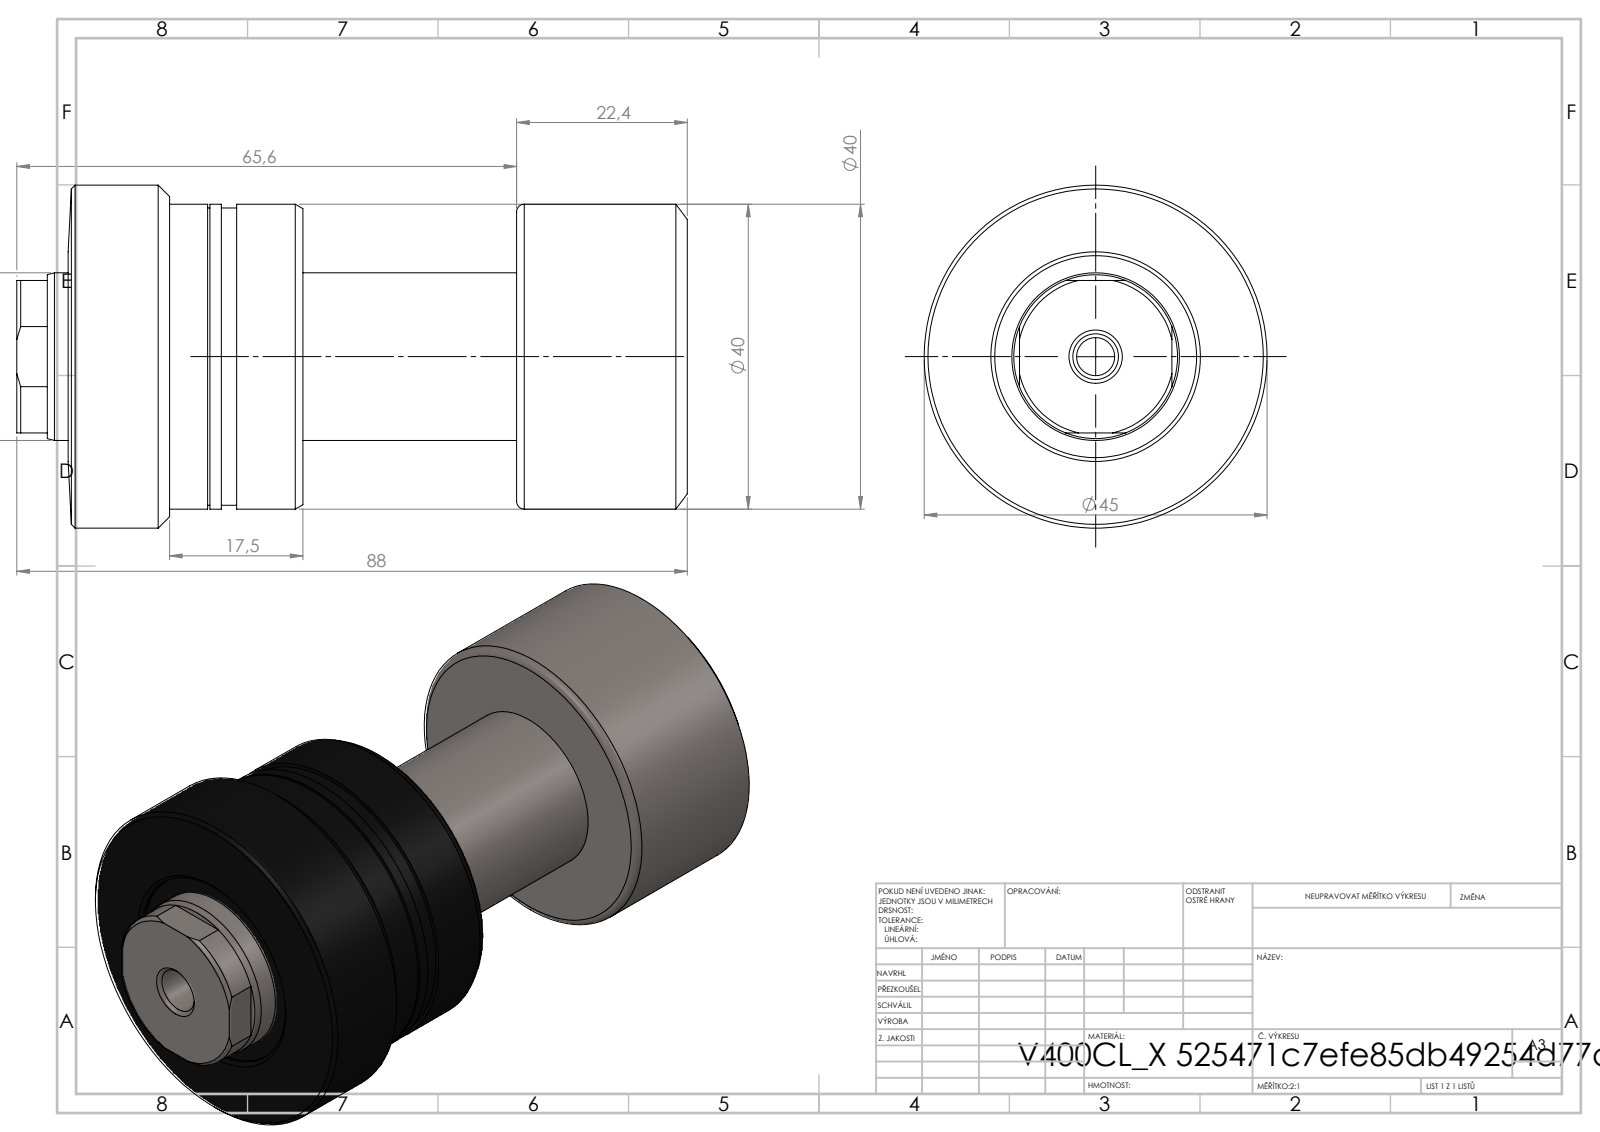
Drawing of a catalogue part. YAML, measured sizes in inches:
part_name: "V400CL_PC_X; V400CL_VC_X"
step_written_by: "SolidWorks 2019 (CONFIG_CONTROL_DESIGN)"
units: inches
bodies: {solids: 2, faces: 79, planar: 19, cylindrical: 30, other: 30}
overall_size: [3.465, 1.772, 1.772]
volume: 5.055
surface_area: 28.81
round_holes:
  - {diameter: 0.081, count: 1}
  - {diameter: 0.197, count: 1}
  - {diameter: 0.236, count: 1}
  - {diameter: 0.866, count: 1}
  - {diameter: 1.043, count: 1}
round_bosses_or_shafts:
  - {diameter: 1.772, count: 1}
  - {diameter: 1.575, count: 1}
  - {diameter: 1.535, count: 1}
partial_cylinders:
  - {radius: 0.423, count: 1}
face_to_face_distances: [0.882, 1.986, 1.104, 3.465, 2.583, 1.478, 0.492, 0.689, 3.167, 2.285]
